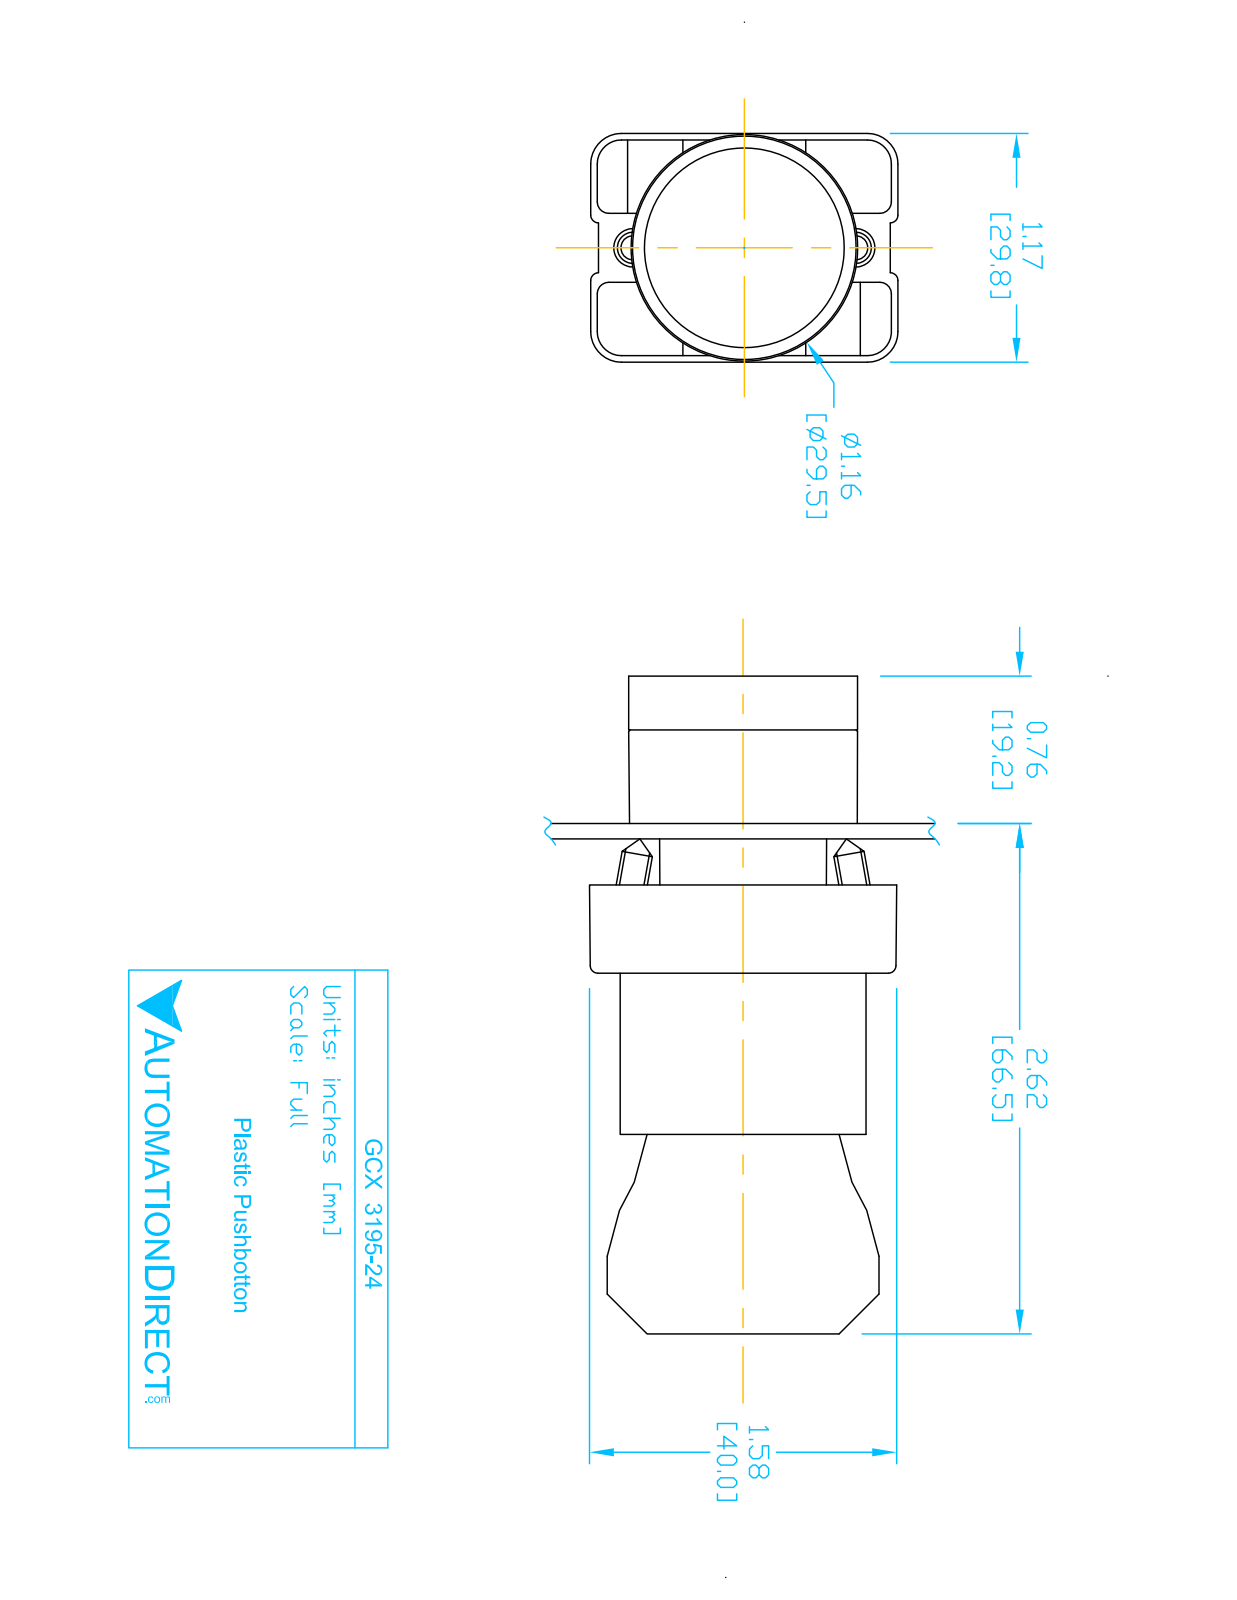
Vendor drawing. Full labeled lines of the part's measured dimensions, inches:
Part name (STEP PRODUCT): GCX3195-24; ECX1050; CONTACT BLOCK; ECX3029-2 (+1 more)
STEP written by: SolidWorks 2016 (AUTOMOTIVE_DESIGN)
Units: inches
Bodies: 8 solids, 431 faces (252 planar, 148 cylindrical, 31 other)
Overall size (bounding box): 3.319 × 1.581 × 1.177
Volume: 2.794 in³ · Surface area: 38.77 in²
Round holes (diameter × count): ⌀0.079 ×2, ⌀0.124 ×2, ⌀0.13 ×2, ⌀0.087 ×1, ⌀0.197 ×1, ⌀0.469 ×1, ⌀0.878 ×1, ⌀0.888 ×1, ⌀1.024 ×1
Round bosses / shafts (diameter × count): ⌀0.157 ×4, ⌀1.175 ×1, ⌀1.004 ×1, ⌀0.945 ×1, ⌀0.856 ×1, ⌀0.78 ×1, ⌀0.504 ×1
Partial cylindrical surfaces — rounded edges, fillets, slot ends (radius × count): R0.059 ×24, R0.041 ×12, R0.124 ×12, R0.157 ×12, R0.039 ×8, R0.128 ×2, R0.02 ×1, R0.063 ×1
Main face-to-face distances: 0.827, 0.579, 2.02, 1.193, 1.171, 0.276, 2.295, 1.469, 0.031, 0.033
Hole centre spacings: 0.236, 0.544, 0.472, 0.49
